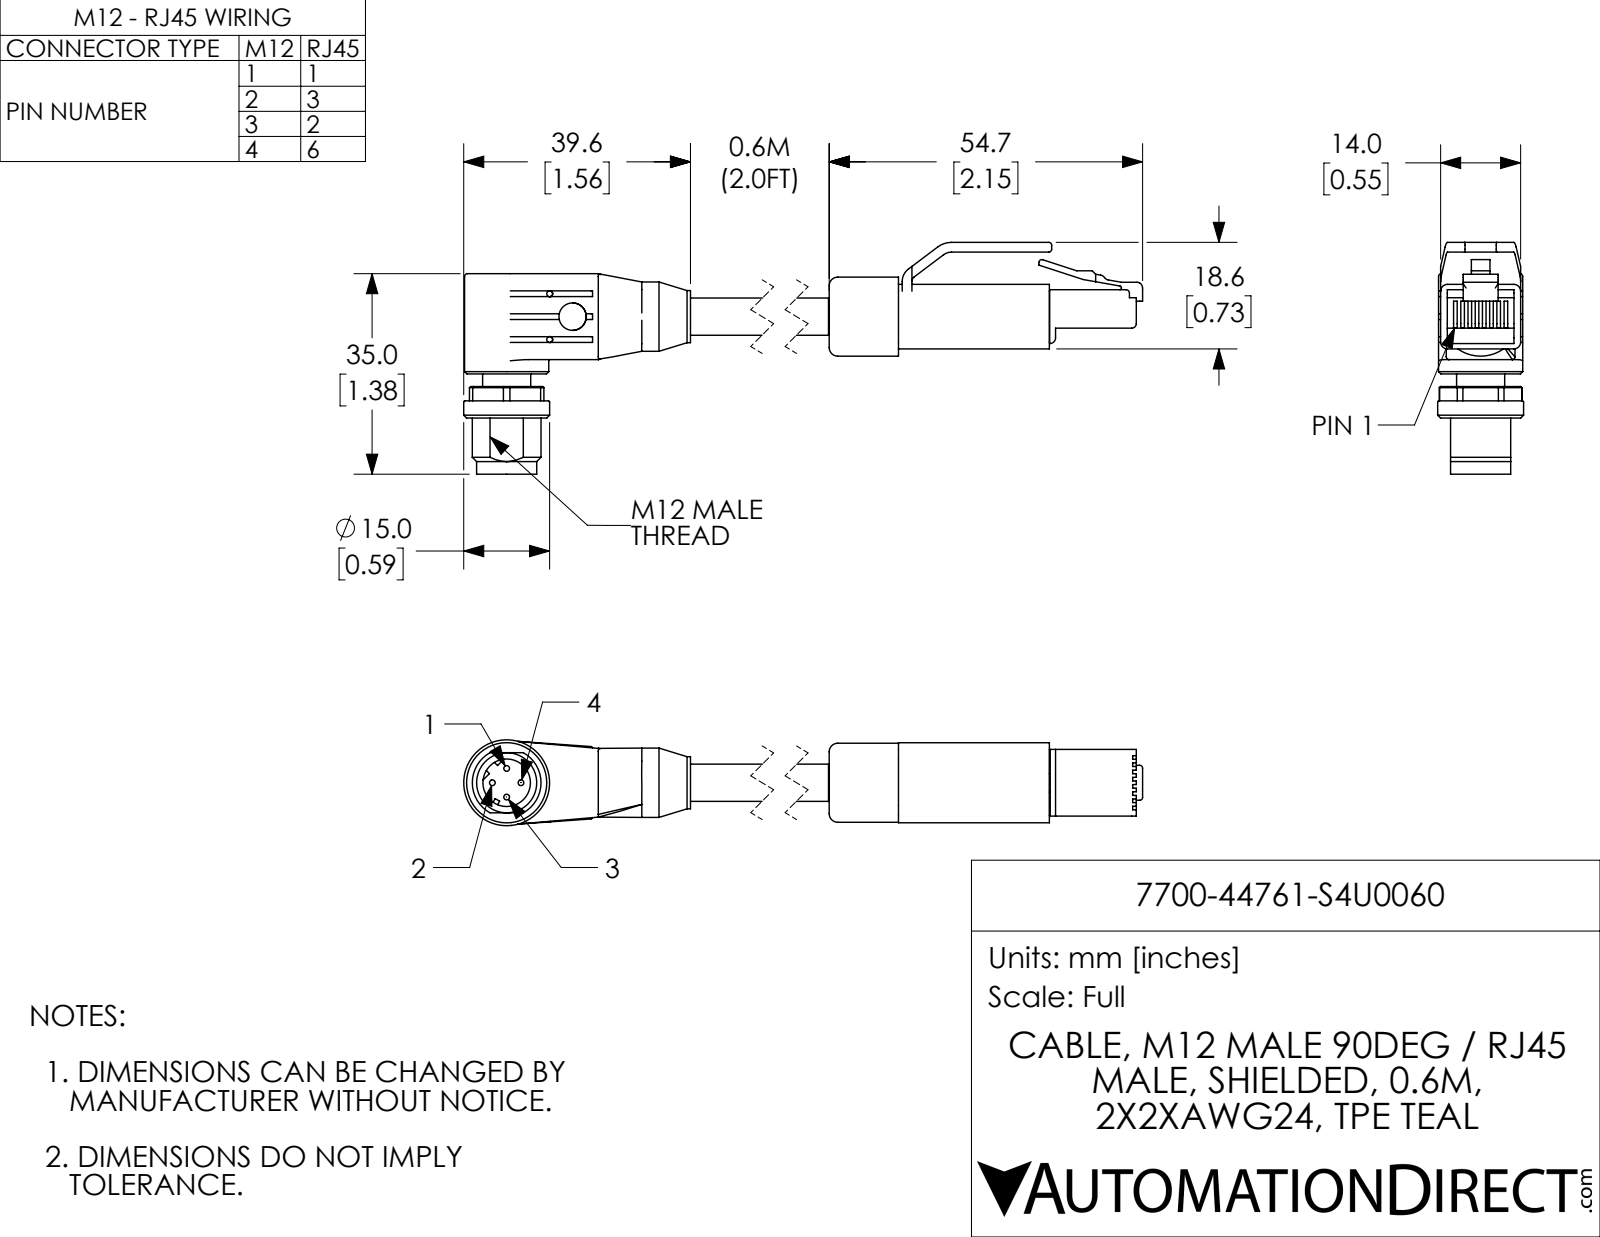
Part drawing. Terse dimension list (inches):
name: 7700-44761-S4U0060; 7700-44761-S4U0060_RJ45; 7700-44761-S4U0060_MALE90
written by: SolidWorks 2017 (AUTOMOTIVE_DESIGN)
unit: in
bodies: 4 solids, 288 faces (163 planar, 83 cylindrical, 42 other)
size: 5.45 × 1.593 × 0.591
volume: 1.047 in³; area: 12.35 in²
holes: 4× ⌀0.041, 1× ⌀0.189, 1× ⌀0.327
bosses: 4× ⌀0.039, 1× ⌀0.591, 1× ⌀0.579, 1× ⌀0.543, 1× ⌀0.476, 1× ⌀0.413, 1× ⌀0.358, 1× ⌀0.331
rounds: 9× R0.02, 6× R0.047, 5× R0.039, 4× R0.012, 1× R0.024, 1× R0.031, 1× R0.091, 1× R0.106
face distances: 0.073, 0.517, 0.444, 0.55, 0.067, 0.258, 0.665, 0.143, 0.301, 0.374
hole spacings: 0.315
